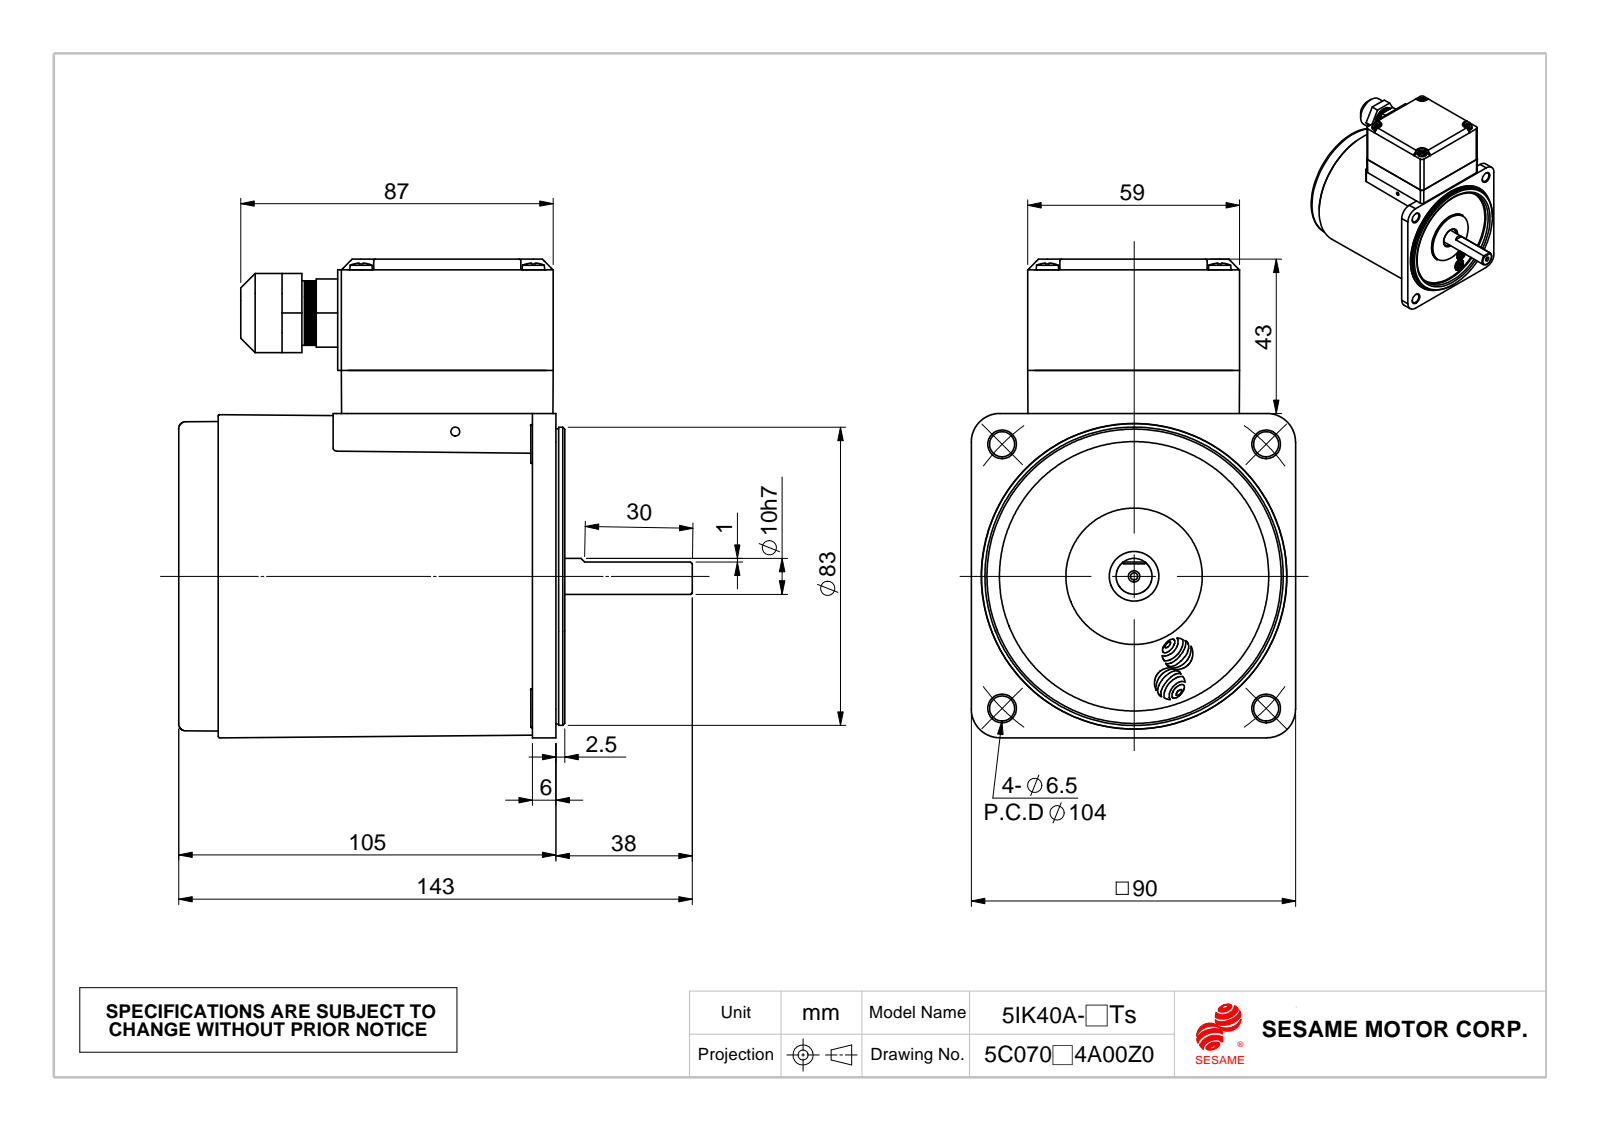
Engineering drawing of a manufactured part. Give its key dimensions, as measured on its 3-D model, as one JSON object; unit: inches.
{"part_name": "M540Ts; 40A; 成品180度; Ts下墊片", "step_written_by": "SolidWorks 2010 (CONFIG_CONTROL_DESIGN)", "units": "inches", "bodies": {"solids": 11, "faces": 2539, "planar": 210, "cylindrical": 930, "other": 1399}, "overall_size": [5.63, 5.248, 3.555], "volume_in3": 18.84, "surface_area_in2": 194.8, "round_holes": [[0.13, 4], [0.138, 4], [0.154, 4], [0.169, 4], [0.276, 4], [0.079, 1], [0.098, 1], [0.433, 1], [0.472, 1], [0.539, 1], [0.571, 1], [0.827, 1]], "round_bosses_or_shafts": [[0.248, 4], [0.118, 4], [3.316, 1], [3.268, 1], [3.236, 1], [1.496, 1], [1.378, 1], [0.866, 1]], "partial_cylinders_radius": [[0.079, 12], [0.02, 8], [0.031, 8], [0.059, 8], [0.065, 8], [0.115, 8], [0.157, 6], [0.008, 4]], "face_to_face_distances": [0.039, 0.472, 4.035, 3.858, 4.075, 0.059, 0.098, 3.898, 0.03, 3.996], "hole_center_spacings": [1.89, 2.047, 2.895, 0.459, 0.486, 0.5, 0.981, 0.984]}
